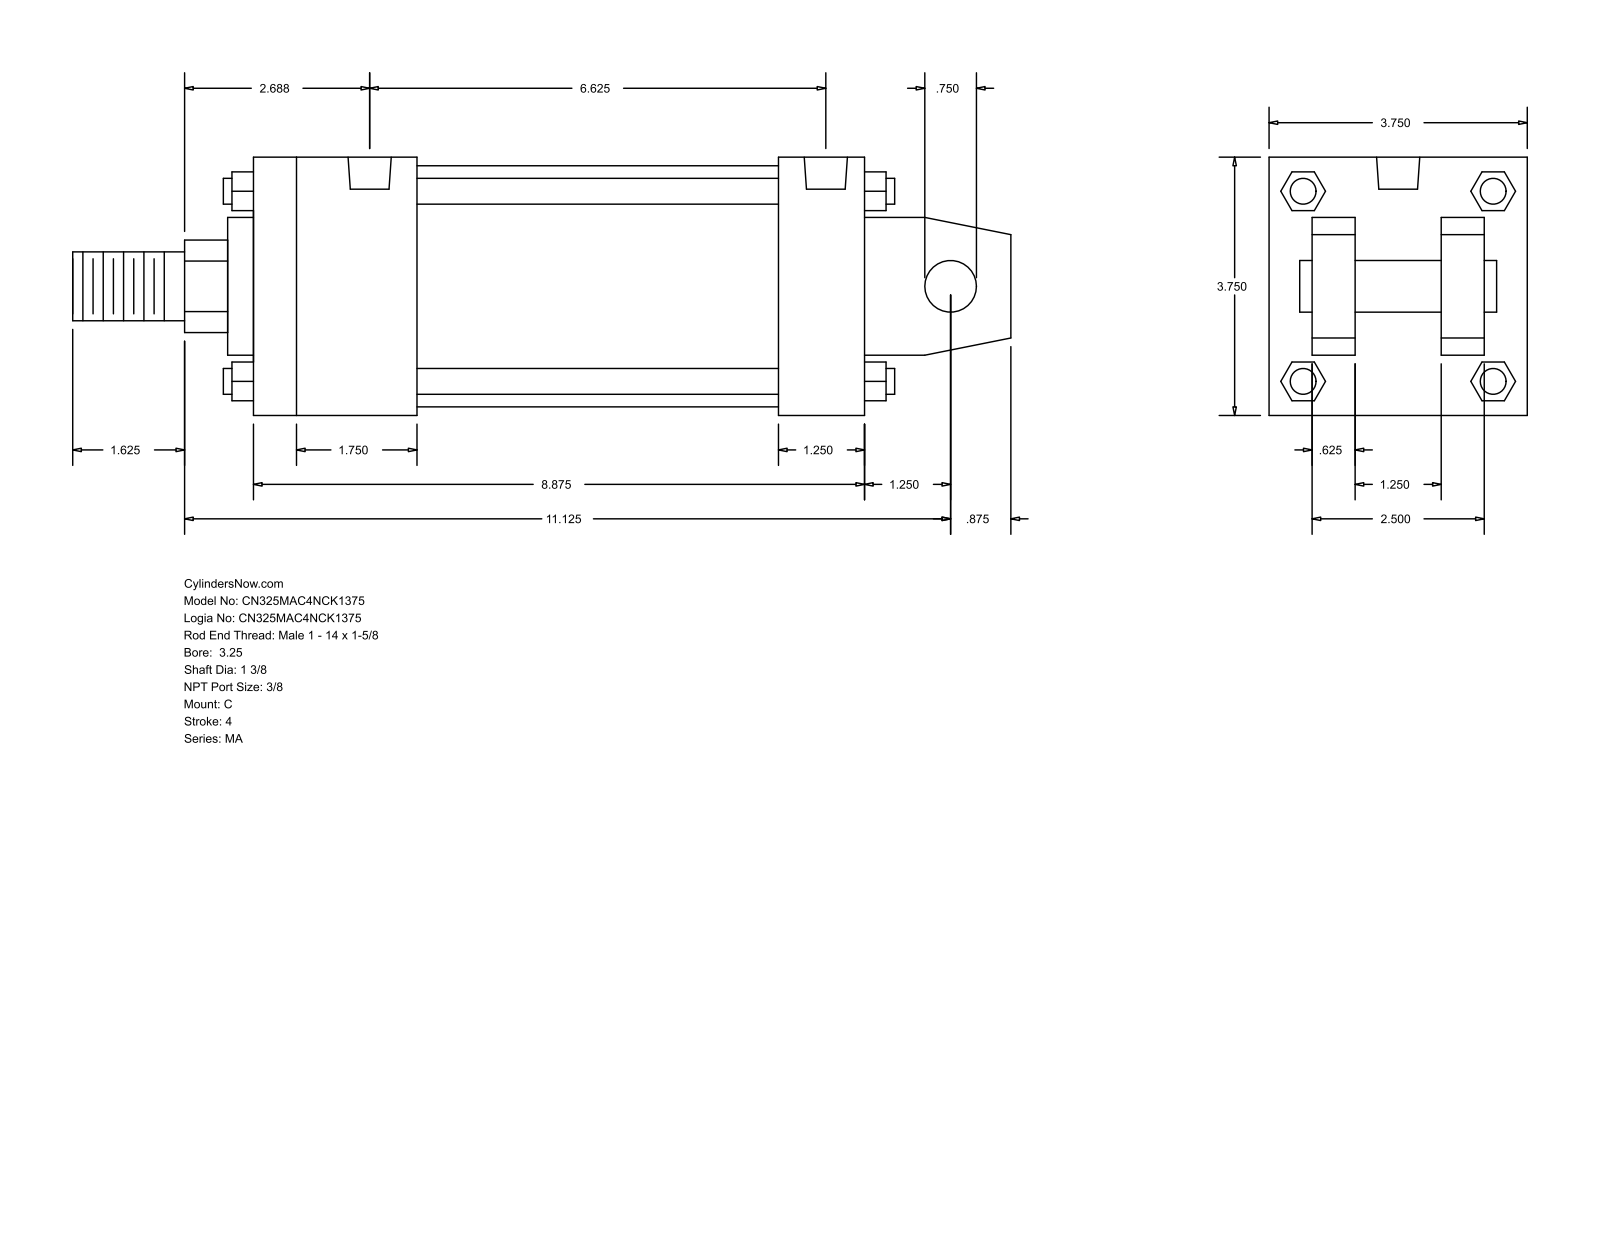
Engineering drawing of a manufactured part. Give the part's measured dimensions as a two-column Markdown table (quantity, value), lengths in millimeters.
| quantity | value |
| --- | --- |
| part name | MA_C__0325_1.375 |
| STEP written by | GSSL Pune (CONFIG_CONTROL_DESIGN) |
| units | millimeters |
| bodies | 0 solids, 139 faces (108 planar, 31 cylindrical, 0 other) |
| overall size | 346.07 × 95.25 × 95.25 |
| round holes (diameter × count) | 11.11 × 4, 15.93 × 2 |
| round bosses / shafts (diameter × count) | 9.53 × 4, 88.9 × 1, 50.8 × 1, 34.92 × 1, 25.4 × 1, 19.05 × 1 |
| partial cylindrical surfaces (radius × count) | 17.06 × 1 |
| main face-to-face distances | 95.24, 15.87, 63.5, 225.42, 31.74, 79.37, 47.63, 193.67, 31.75, 60.32 |
| hole center spacings | 158.75, 4.76, 4.77, 163.51, 163.52, 168.28 |
